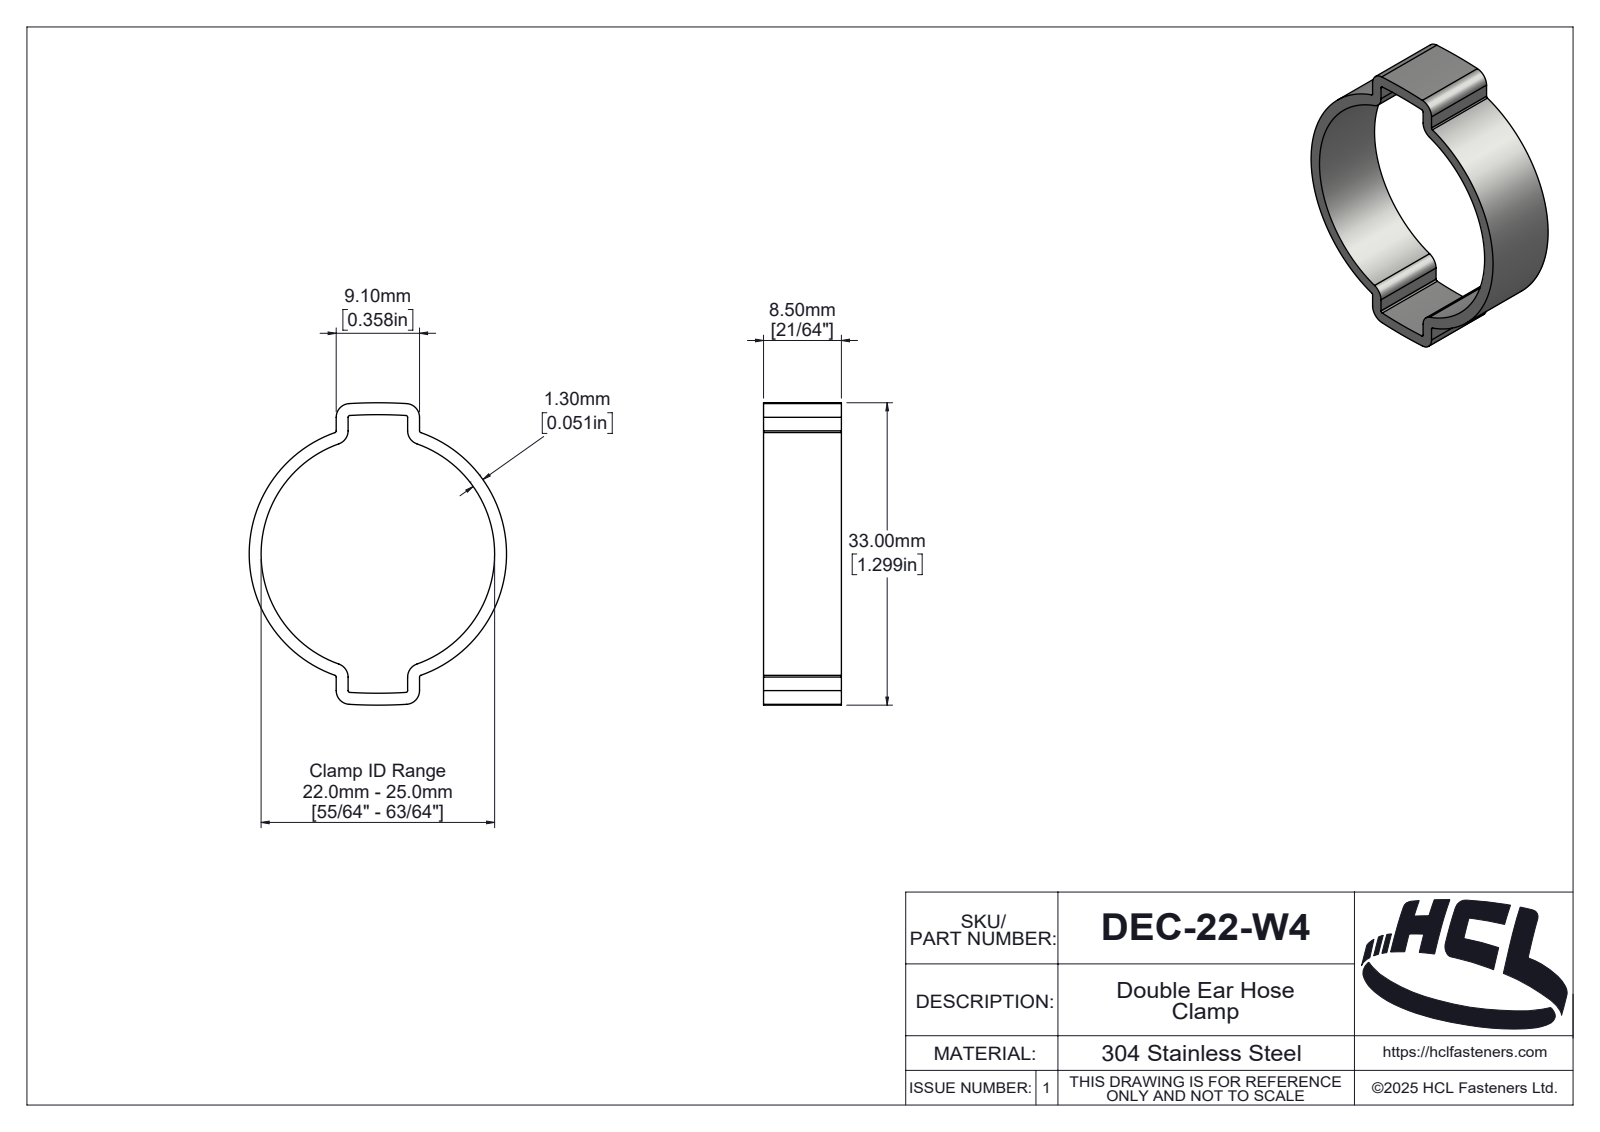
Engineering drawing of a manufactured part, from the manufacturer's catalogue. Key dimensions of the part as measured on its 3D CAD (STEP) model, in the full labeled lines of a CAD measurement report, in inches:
Part name (STEP PRODUCT): DEC-22-W4
STEP written by: SolidWorks 2025 (AUTOMOTIVE_DESIGN)
Units: inches
Bodies: 1 solid, 137 faces (12 planar, 67 cylindrical, 58 other)
Overall size (bounding box): 1.299 × 1.106 × 0.335
Volume: 0.063 in³ · Surface area: 2.85 in²
Partial cylindrical surfaces — rounded edges, fillets, slot ends (radius × count): R0.008 ×8, R0.059 ×8, R2.081 ×2, R2.132 ×2, R0.008 ×1, R0.032 ×1, R0.04 ×1, R0.042 ×1
Main face-to-face distances: 0.335, 0.051, 0.307, 0.358, 0.256, 0.174, 0.123, 0.133, 0.184, 0.169
